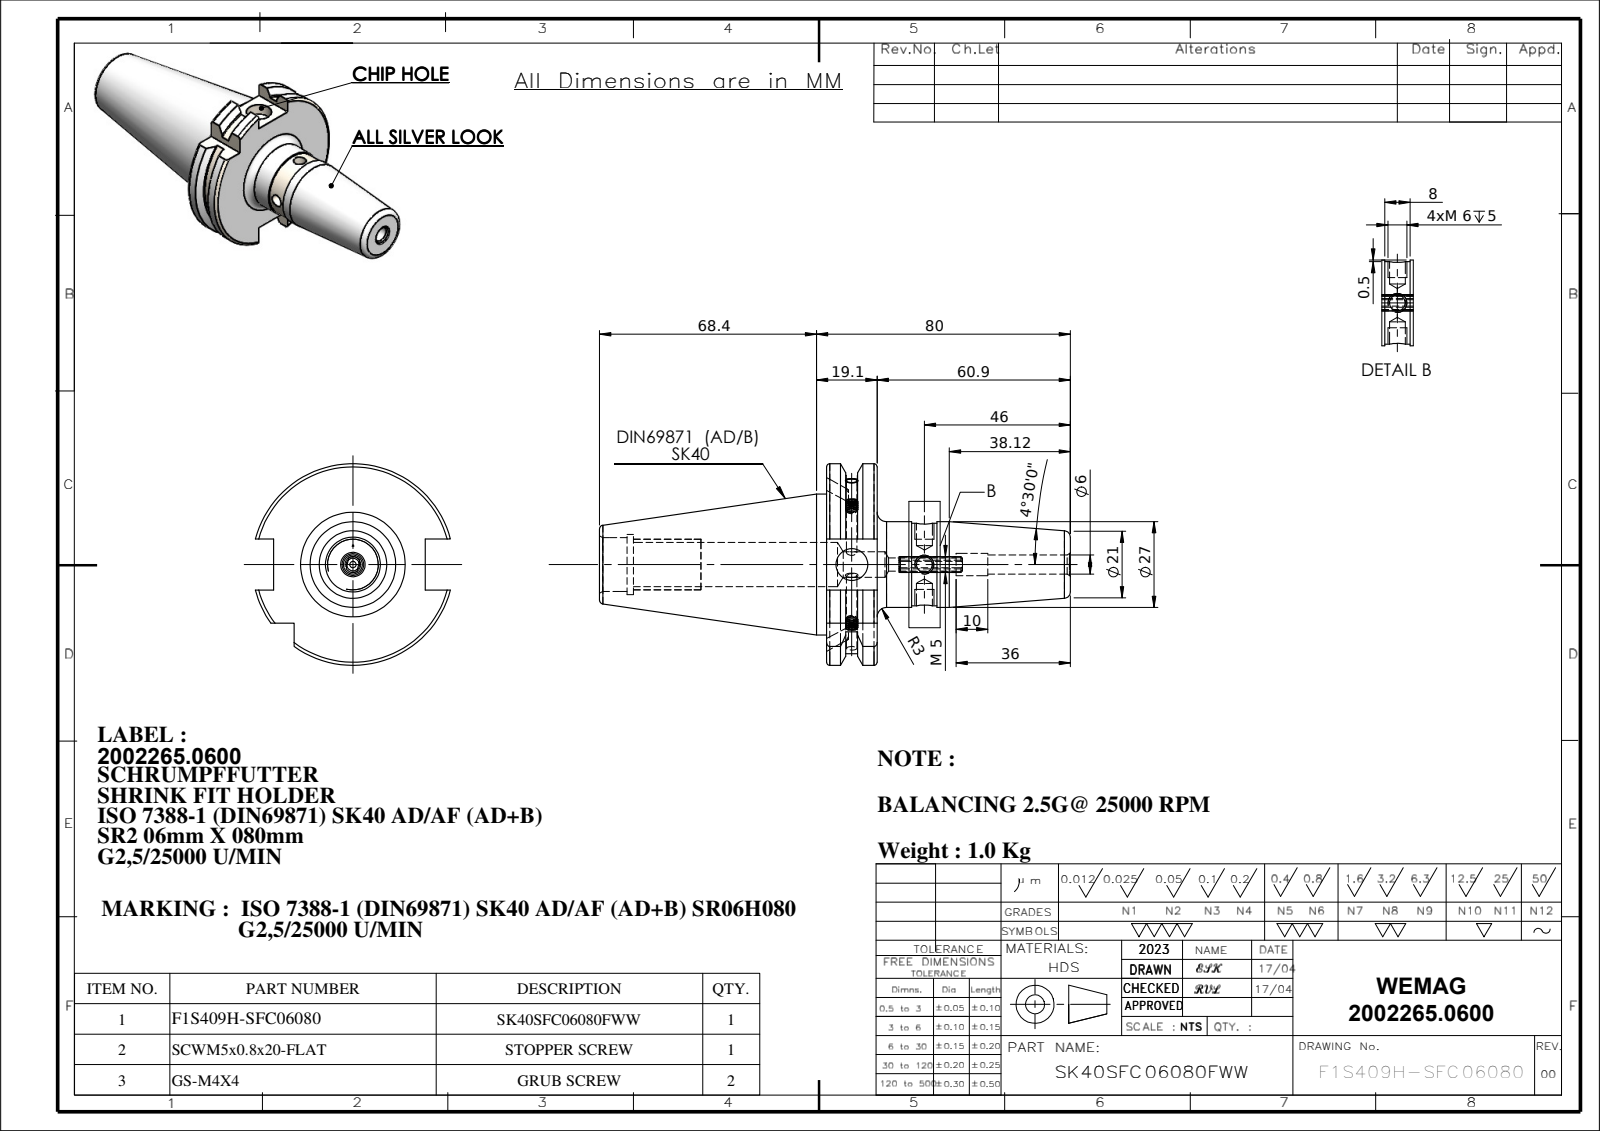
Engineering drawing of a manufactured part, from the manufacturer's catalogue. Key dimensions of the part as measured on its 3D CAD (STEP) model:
Part name (STEP PRODUCT): 91406-SR206080; SK40SFC06080FWW; GS-M4X4_DIN 913 - M4 x 4-N; SCWM5x0.8x20-FLAT
STEP written by: SolidWorks 2018 (CONFIG_CONTROL_DESIGN)
Units: millimetres
Bodies: 4 solids, 239 faces (54 planar, 73 cylindrical, 112 other)
Overall size (bounding box): 148.4 × 63.55 × 61.48
Volume: 127 795 mm³ · Surface area: 27 987 mm²
Round holes (diameter × count): ⌀5 ×2, ⌀2 ×1, ⌀3.3 ×1, ⌀4.2 ×1, ⌀5.99 ×1, ⌀6.99 ×1, ⌀8 ×1, ⌀10 ×1, ⌀14 ×1, ⌀17 ×1, ⌀19 ×1
Round bosses / shafts (diameter × count): ⌀4 ×2, ⌀44.45 ×1, ⌀27 ×1, ⌀26 ×1
Partial cylindrical surfaces — rounded edges, fillets, slot ends (radius × count): R2.5 ×1, R28.12 ×1, R31.77 ×1
Main face-to-face distances: 15.9, 60.9, 76.8, 16.1, 47.8, 3.5, 71.6, 87.5, 148.4, 10.7
Hole centre spacings: 22.85
